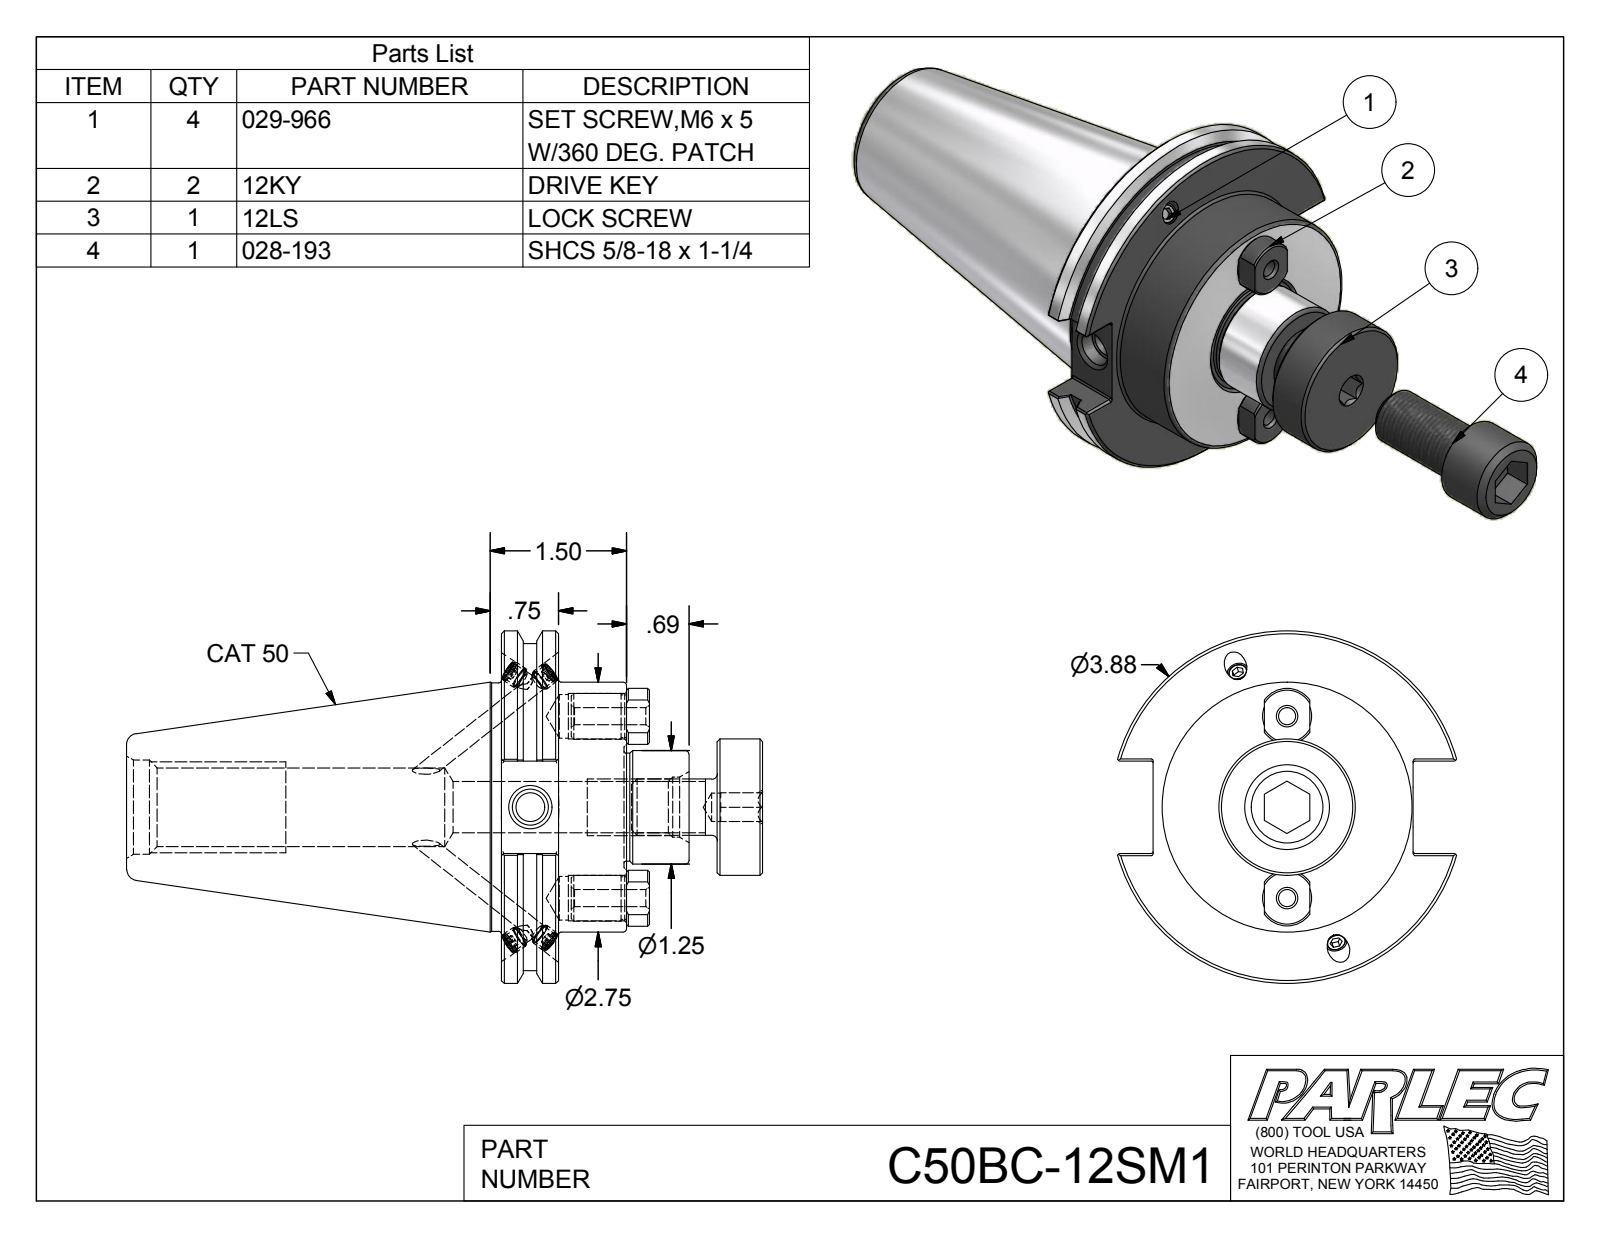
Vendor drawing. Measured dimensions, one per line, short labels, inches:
name: C50BC-12SM1; C50BC-12SM1-1; 028-193; 12KY (+2 more)
written by: Autodesk Inventor 2012 (AUTOMOTIVE_DESIGN)
unit: in
bodies: 9 solids, 253 faces (111 planar, 67 cylindrical, 75 other)
size: 9.487 × 3.875 × 3.729
volume: 26.41 in³; area: 103.7 in²
holes: 4× ⌀0.197, 4× ⌀0.24, 2× ⌀0.19, 2× ⌀0.48, 2× ⌀0.5, 1× ⌀0.312, 1× ⌀0.315, 1× ⌀0.399, 1× ⌀0.565, 1× ⌀0.66, 1× ⌀0.865, 1× ⌀1.038
bosses: 4× ⌀0.244, 4× ⌀0.236, 2× ⌀0.505, 2× ⌀0.47, 1× ⌀3.875, 1× ⌀3.594, 1× ⌀2.75, 1× ⌀2.73
rounds: 12× R0.02, 2× R0.308
face distances: 0.625, 1.375, 0.75, 2.872, 2.247, 1.497, 0.5, 2.372, 1.747, 0.997
hole spacings: 1, 2
